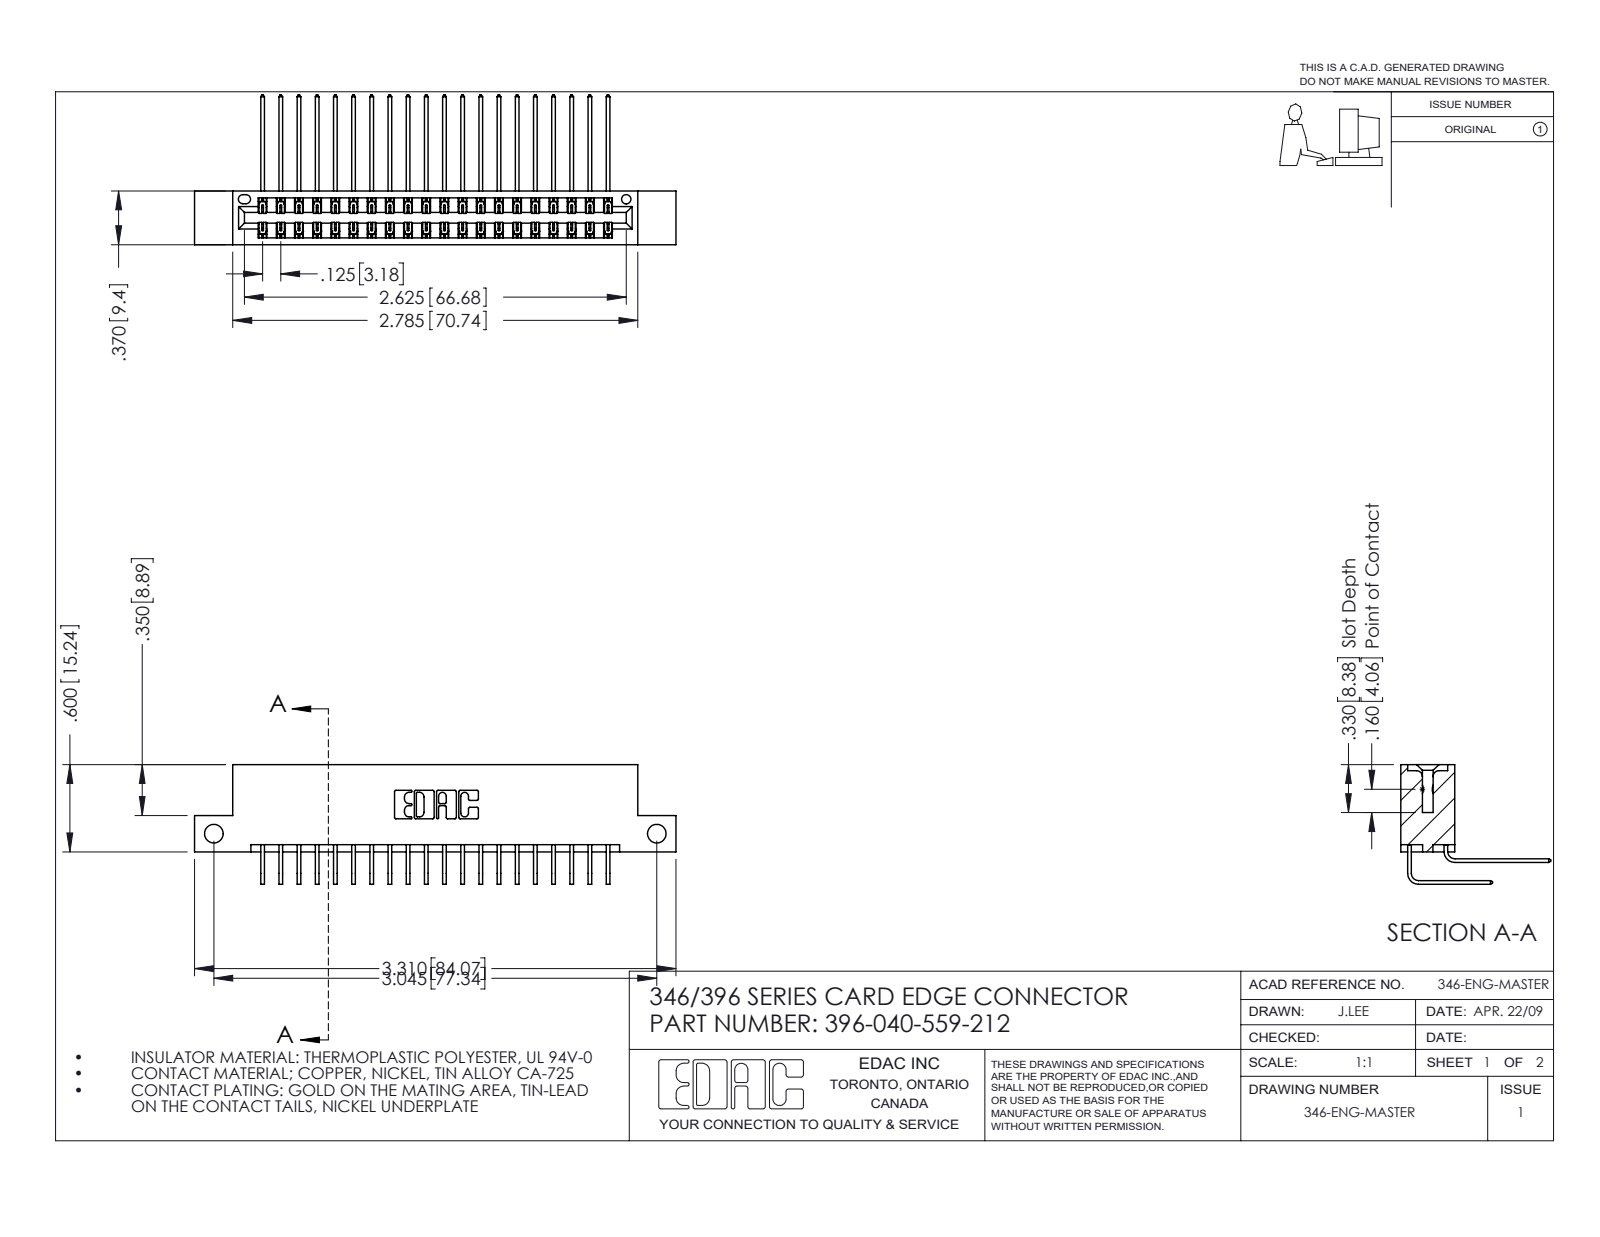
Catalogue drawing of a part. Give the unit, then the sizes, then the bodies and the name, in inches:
Units: inches
Overall size (bounding box): 3.31 × 1.03 × 0.823
Round holes (diameter × count): ⌀0.128 ×2, ⌀0.064 ×1
Partial cylindrical surfaces — rounded edges, fillets, slot ends (radius × count): R0.006 ×60, R0.01 ×22, R0.007 ×6, R0.031 ×6, R0.026 ×3, R0.014 ×2, R0.022 ×2, R0.024 ×2
Main face-to-face distances: 0.048, 0.322, 0.25, 0.025, 0.37, 0.072, 0.298, 0.275, 0.148, 0.222
Hole centre spacings: 3.045
Volume: 0.499 in³ · Surface area: 18.38 in²
Bodies: 41 solids, 2282 faces (1556 planar, 726 cylindrical, 0 other)
Part name (STEP PRODUCT): 346 Part_Flush Mounting Lugs - Side Mount; 345-292-001_558 559 Tail - 1; 396-040-559-212; 345-292-001_559 Tail - 2
STEP written by: SolidWorks 2016 (CONFIG_CONTROL_DESIGN)
